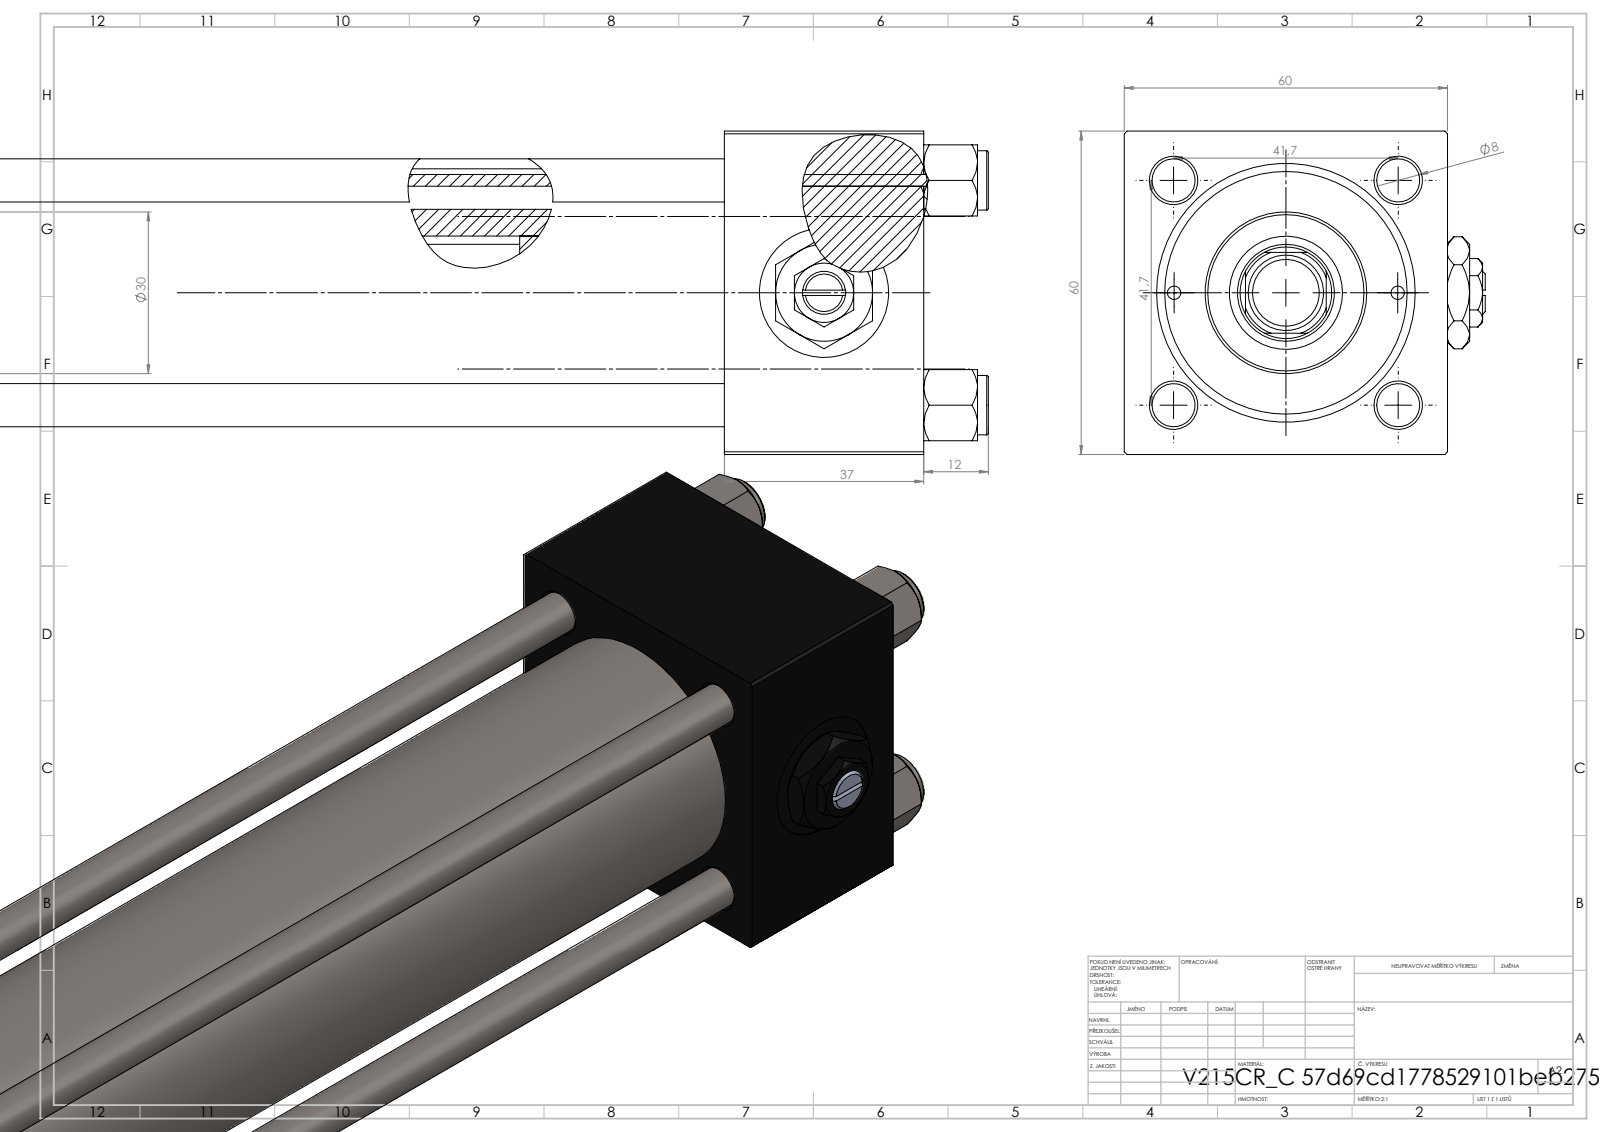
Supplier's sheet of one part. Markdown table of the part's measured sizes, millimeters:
| quantity | value |
| --- | --- |
| part name | Zatka_pro_OIL_PORT; ROD_END_AH; V215CR_VCP_C; V215CR_C_Body (+3 more) |
| STEP written by | SolidWorks 2019 (CONFIG_CONTROL_DESIGN) |
| units | millimeters |
| bodies | 14 solids, 1270 faces (580 planar, 106 cylindrical, 584 other) |
| overall size | 343 × 67 × 60 |
| volume | 522 457 mm³ |
| surface area | 169 269 mm² |
| round holes (diameter × count) | 8 × 4, 2.5 × 2, 7 × 2, 16.66 × 2, 24 × 2, 8.5 × 1, 18 × 1, 21 × 1, 31 × 1, 40 × 1, 45 × 1 |
| round bosses / shafts (diameter × count) | 11 × 4, 46 × 1, 30 × 1, 14 × 1, 12 × 1 |
| partial cylindrical surfaces (radius × count) | 8.5 × 1 |
| main face-to-face distances | 60, 37, 288, 251, 53, 235, 198, 259.3, 222.3, 24.3 |
| hole center spacings | 20.85, 29.49, 41.7, 46.53, 20.75, 58.97, 41.5, 232.5 |
